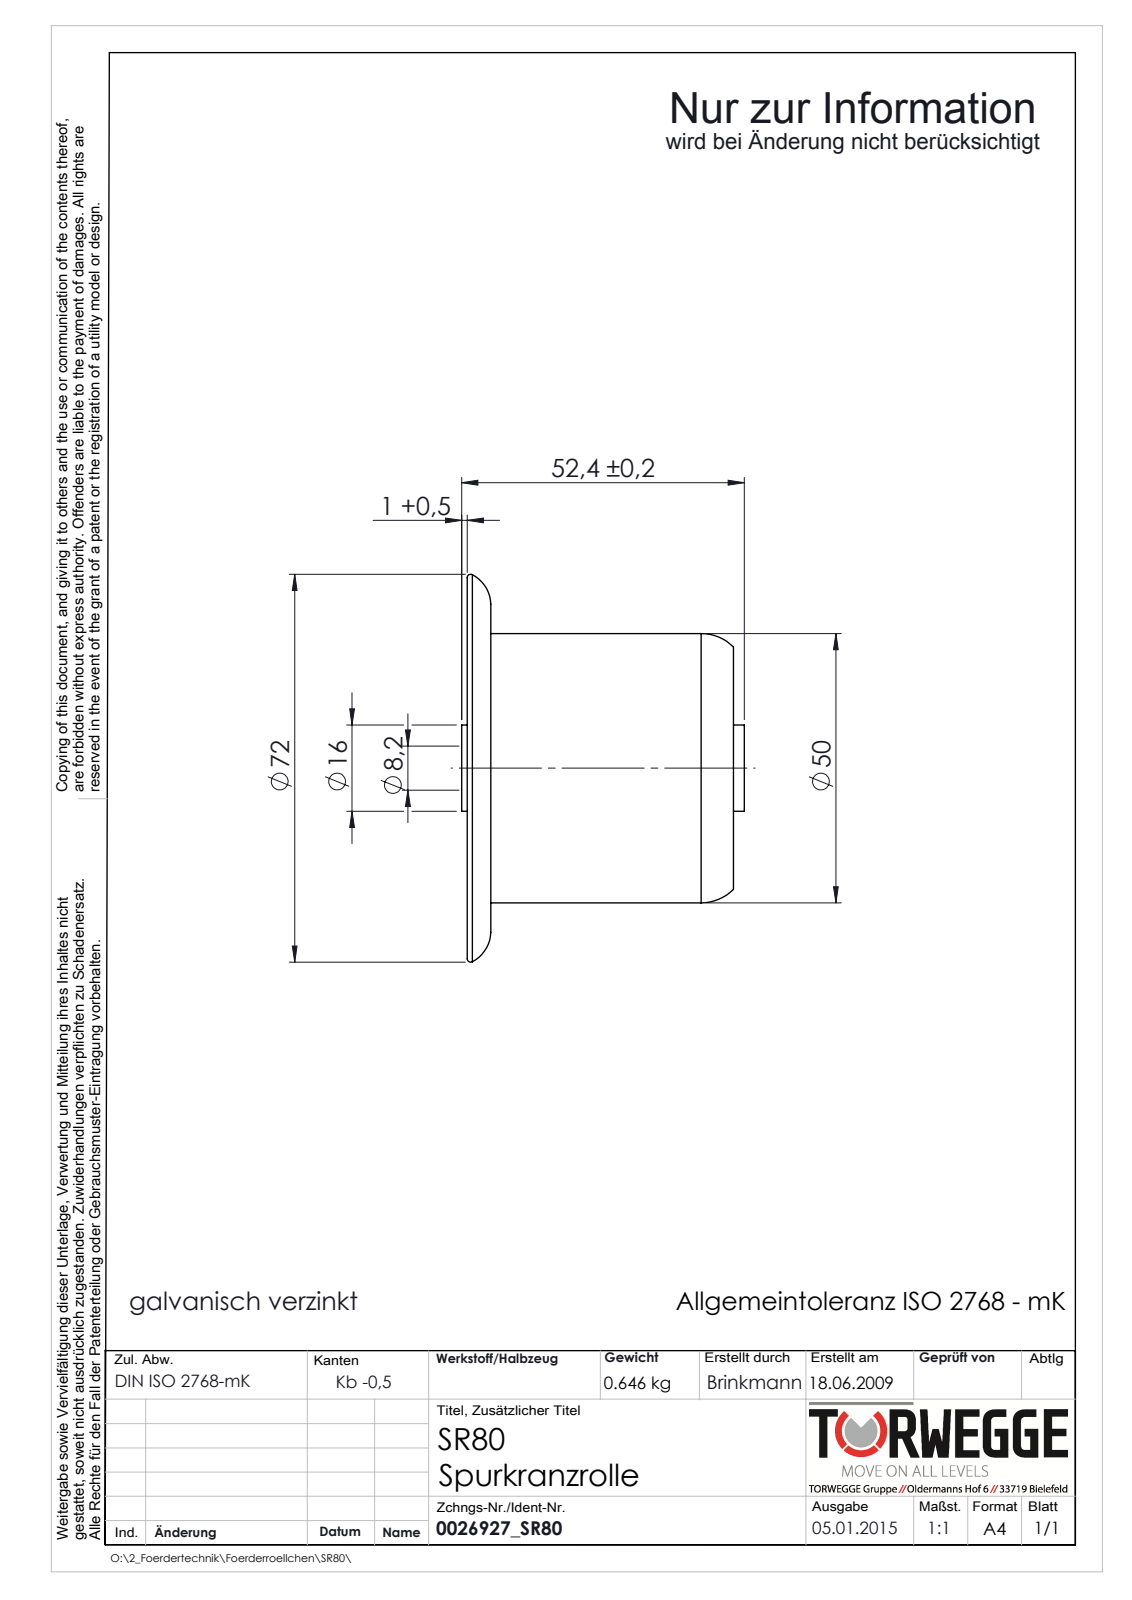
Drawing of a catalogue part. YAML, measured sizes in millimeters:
part_name: "0026927_SR80"
step_written_by: "SolidWorks 2014 (AUTOMOTIVE_DESIGN)"
units: millimeters
bodies: {solids: 1, faces: 56, planar: 10, cylindrical: 18, other: 28}
overall_size: [72, 72, 52.4]
volume: 82118
surface_area: 20389
round_holes:
  - {diameter: 8.2, count: 1}
  - {diameter: 41, count: 1}
  - {diameter: 45, count: 1}
round_bosses_or_shafts:
  - {diameter: 50, count: 1}
  - {diameter: 49.5, count: 1}
  - {diameter: 29.5, count: 1}
  - {diameter: 16, count: 1}
face_to_face_distances: [1.72, 39.4, 5.1, 6.82, 8, 44.5, 46.22, 46.9, 7.5, 2.4]
